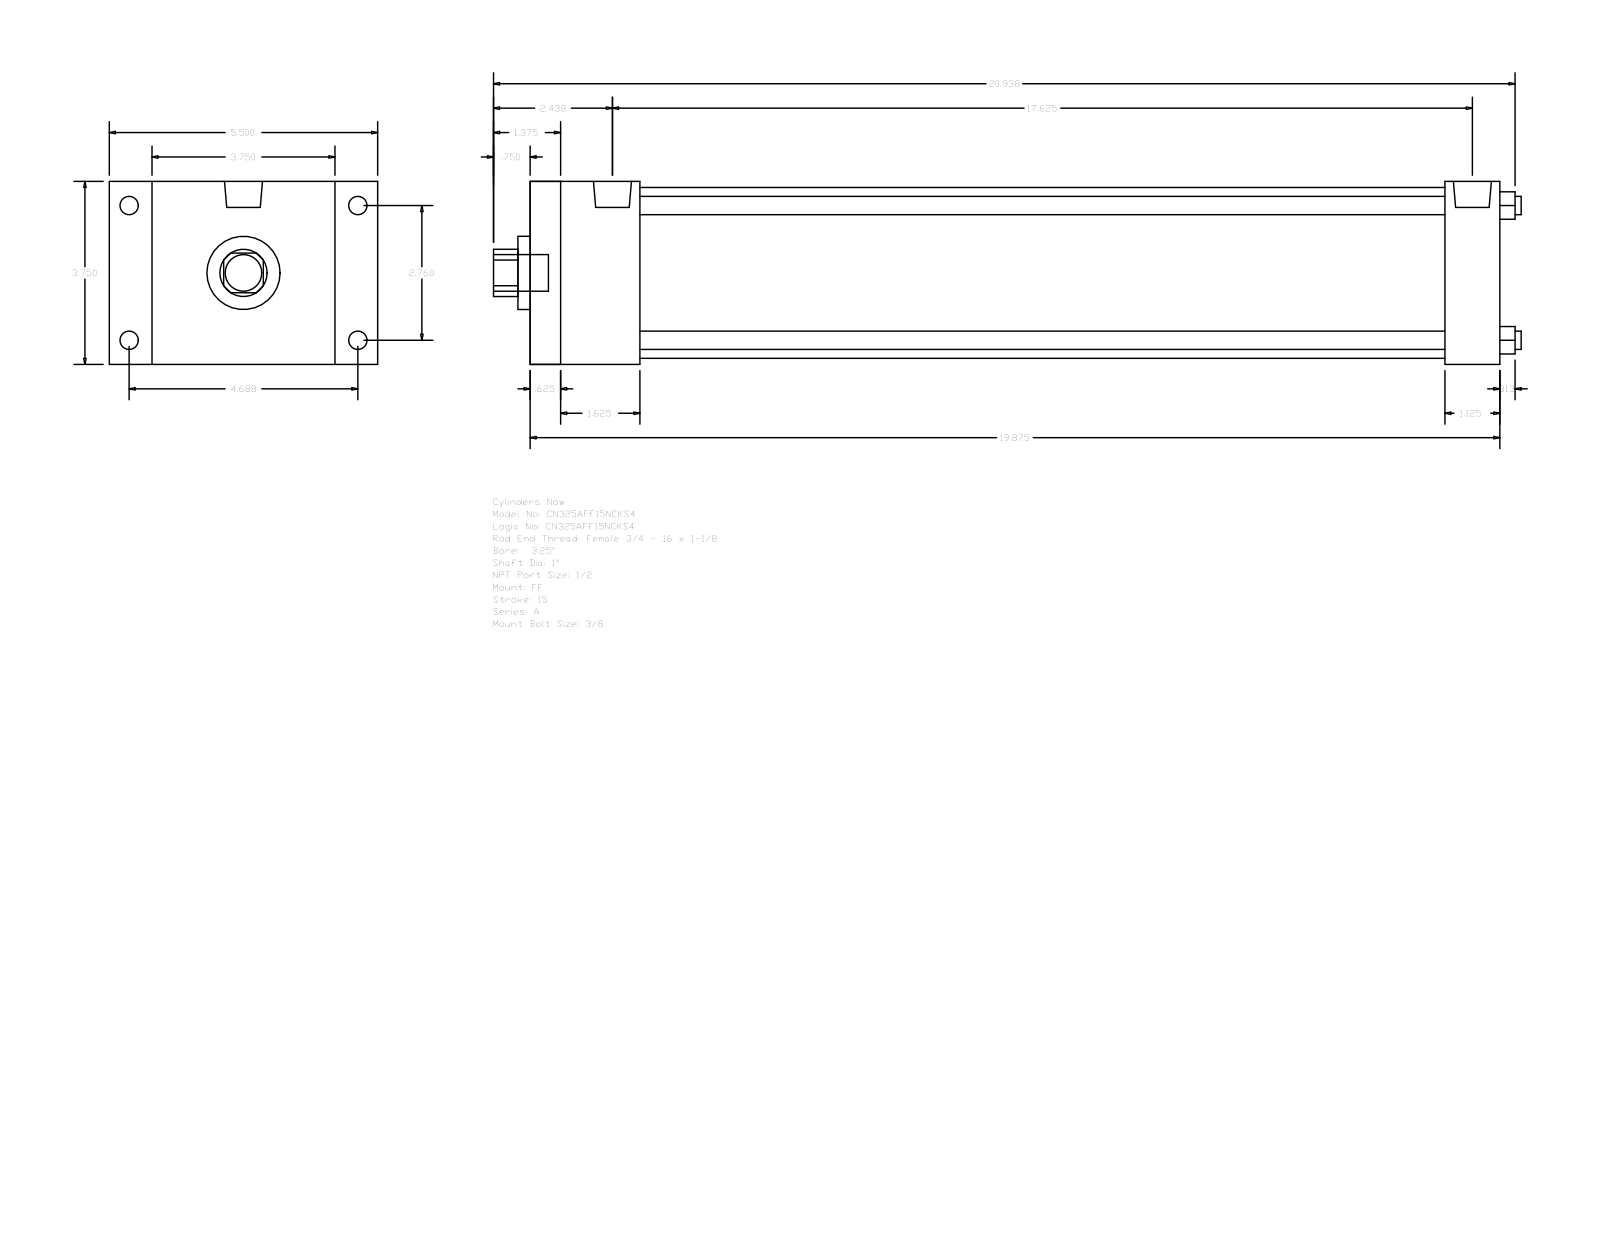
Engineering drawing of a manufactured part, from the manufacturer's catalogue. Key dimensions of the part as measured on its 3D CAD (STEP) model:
Part name (STEP PRODUCT): A_FF__0325_1
STEP written by: GSSL Pune (CONFIG_CONTROL_DESIGN)
Units: millimetres
Bodies: 0 solids, 92 faces (64 planar, 28 cylindrical, 0 other)
Overall size (bounding box): 534.99 × 139.7 × 95.25
Round holes (diameter × count): ⌀9.53 ×4, ⌀25.4 ×1, ⌀38.1 ×1, ⌀88.9 ×1
Round bosses / shafts (diameter × count): ⌀9.53 ×4, ⌀8.73 ×4, ⌀19.77 ×2, ⌀19.05 ×1
Partial cylindrical surfaces — rounded edges, fillets, slot ends (radius × count): R12.29 ×1
Main face-to-face distances: 95.24, 504.83, 15.87, 488.96, 22.23, 117.47, 57.15, 476.25, 41.28, 460.38
Hole centre spacings: 49.57, 70.1, 99.14
